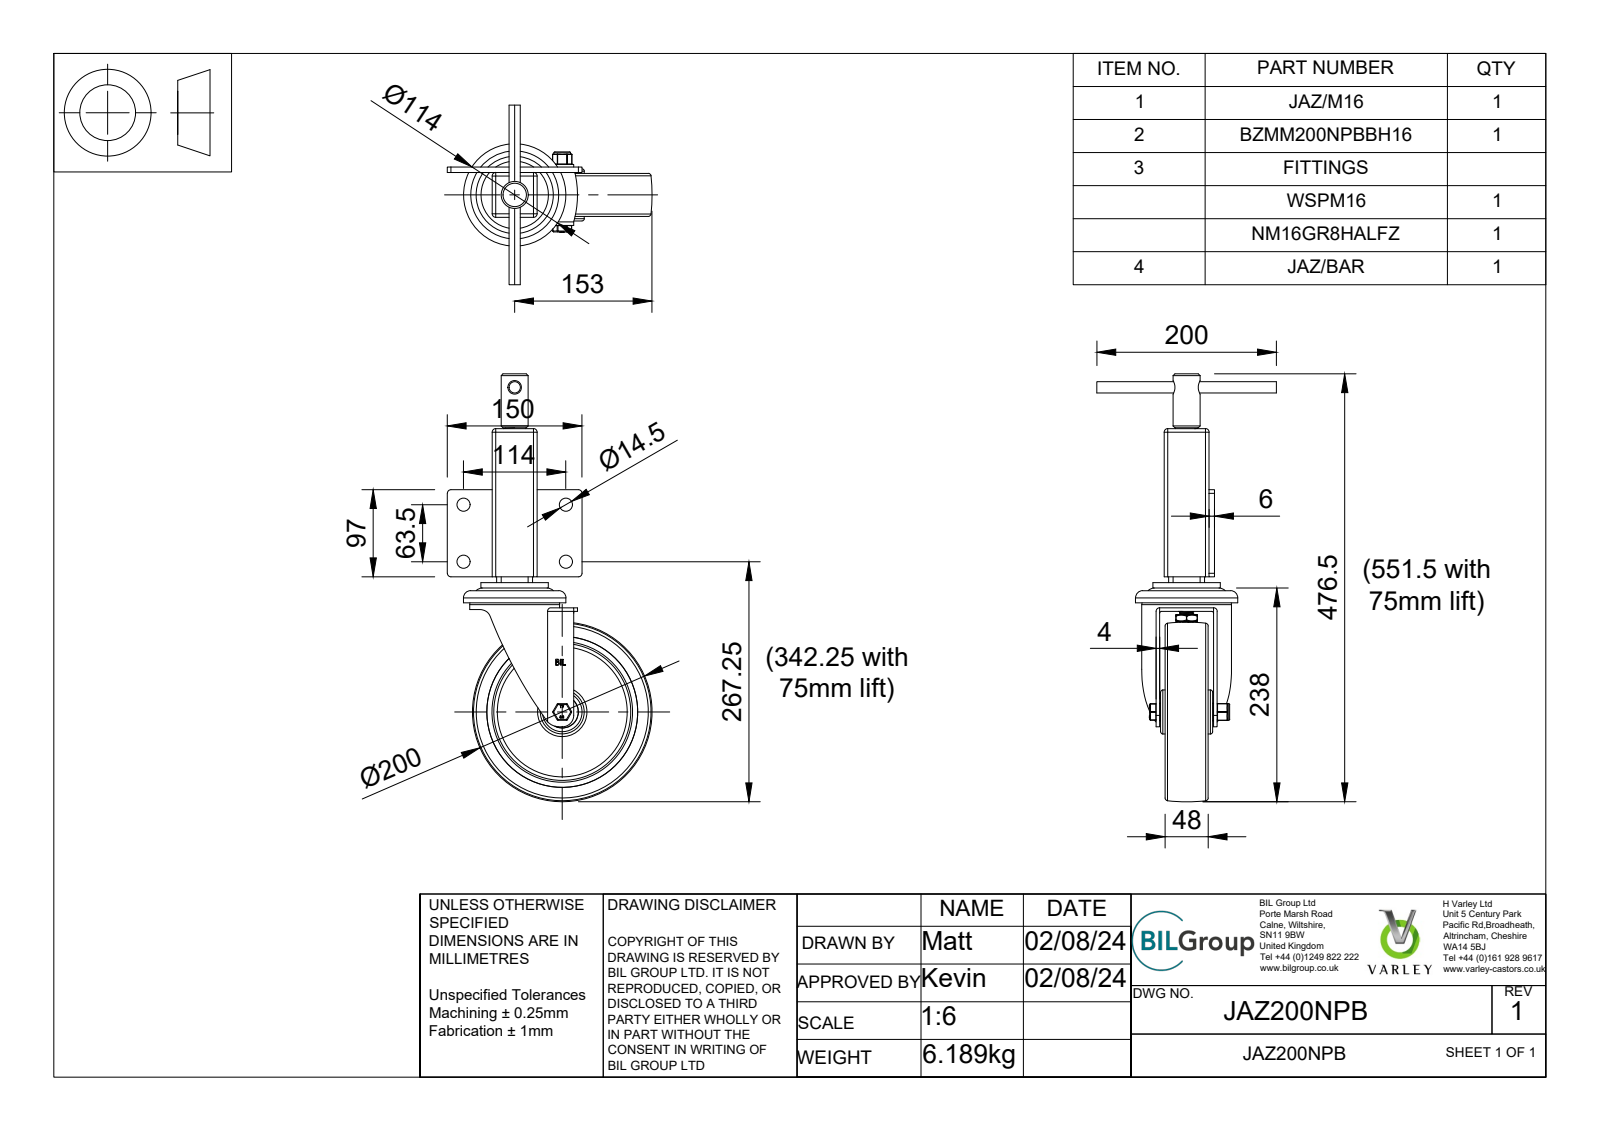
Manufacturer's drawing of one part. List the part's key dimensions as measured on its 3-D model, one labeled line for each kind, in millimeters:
Part name (STEP PRODUCT): JAZ200NPB v3; BZMM200ASBH16 v1; ZINC PLATED, PRESSED STEEL HEAD; ZINC PLATED, PRESSED STEEL FORKS (+8 more)
STEP written by: Autodesk Translation Framework v13.14.0.145 (AUTOMOTIVE_DESIGN)
Units: millimetres
Bodies: 29 solids, 754 faces (298 planar, 305 cylindrical, 151 other)
Overall size (bounding box): 476.5 × 228 × 200
Volume: 1 400 000 mm³ · Surface area: 484 765 mm²
Round holes (diameter × count): ⌀14.5 ×4, ⌀12 ×1, ⌀12.2 ×1, ⌀14 ×1, ⌀15.1 ×1, ⌀16 ×1, ⌀16.2 ×1, ⌀16.5 ×1, ⌀20 ×1, ⌀20.5 ×1, ⌀30 ×1, ⌀36 ×1
Round bosses / shafts (diameter × count): ⌀5 ×10, ⌀114 ×1, ⌀100 ×1, ⌀75 ×1, ⌀74 ×1, ⌀49 ×1, ⌀47 ×1, ⌀35.8 ×1
Partial cylindrical surfaces — rounded edges, fillets, slot ends (radius × count): R0.5 ×24, R4 ×14, R1 ×12, R2.5 ×8, R2 ×4, R5 ×4, R12 ×1, R12.5 ×1
Main face-to-face distances: 2.5, 6, 5, 28, 47.5, 45, 27, 42.5, 1, 22
Hole centre spacings: 63.5, 114, 130.49, 142.59, 202.39, 167.3, 200.18, 230.78
